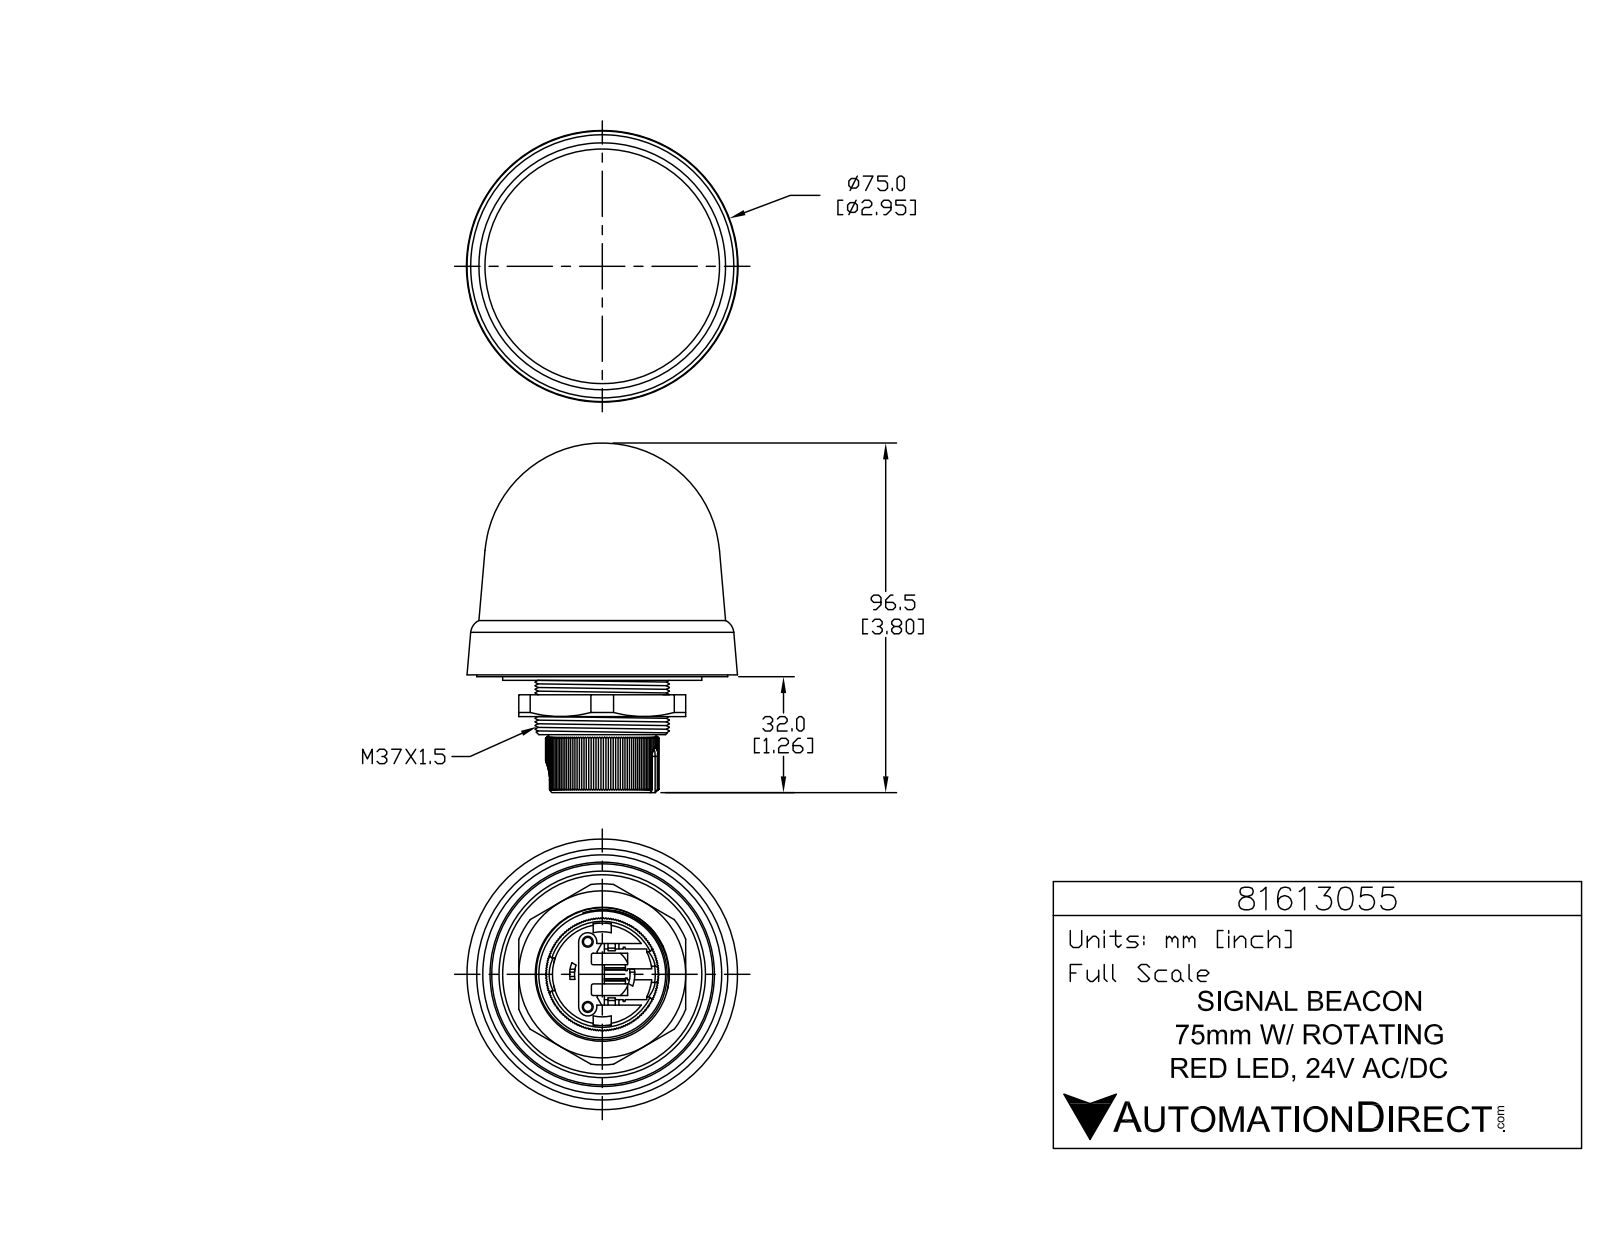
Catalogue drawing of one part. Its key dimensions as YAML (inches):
part_name: "81613055"
step_written_by: "SolidWorks 2019 (CONFIG_CONTROL_DESIGN)"
units: inches
bodies: {solids: 3, faces: 560, planar: 432, cylindrical: 80, other: 48}
overall_size: [3.799, 2.941, 2.941]
volume: 12.36
surface_area: 58.68
round_holes:
  - {diameter: 0.094, count: 2}
  - {diameter: 0.118, count: 2}
  - {diameter: 0.604, count: 1}
  - {diameter: 1.142, count: 1}
round_bosses_or_shafts:
  - {diameter: 0.217, count: 2}
  - {diameter: 0.067, count: 2}
  - {diameter: 2.165, count: 1}
  - {diameter: 1.457, count: 1}
  - {diameter: 0.925, count: 1}
partial_cylinders:
  - {radius: 0.008, count: 6}
  - {radius: 0.039, count: 6}
  - {radius: 0.02, count: 4}
  - {radius: 0.031, count: 2}
  - {radius: 0.079, count: 2}
  - {radius: 0.098, count: 2}
  - {radius: 0.177, count: 1}
  - {radius: 0.354, count: 1}
face_to_face_distances: [0.177, 0.354, 0.197, 0.433, 0.512, 0.335, 0.059, 0.394, 0.118, 0.157]
hole_center_spacings: [0.388, 0.709]
